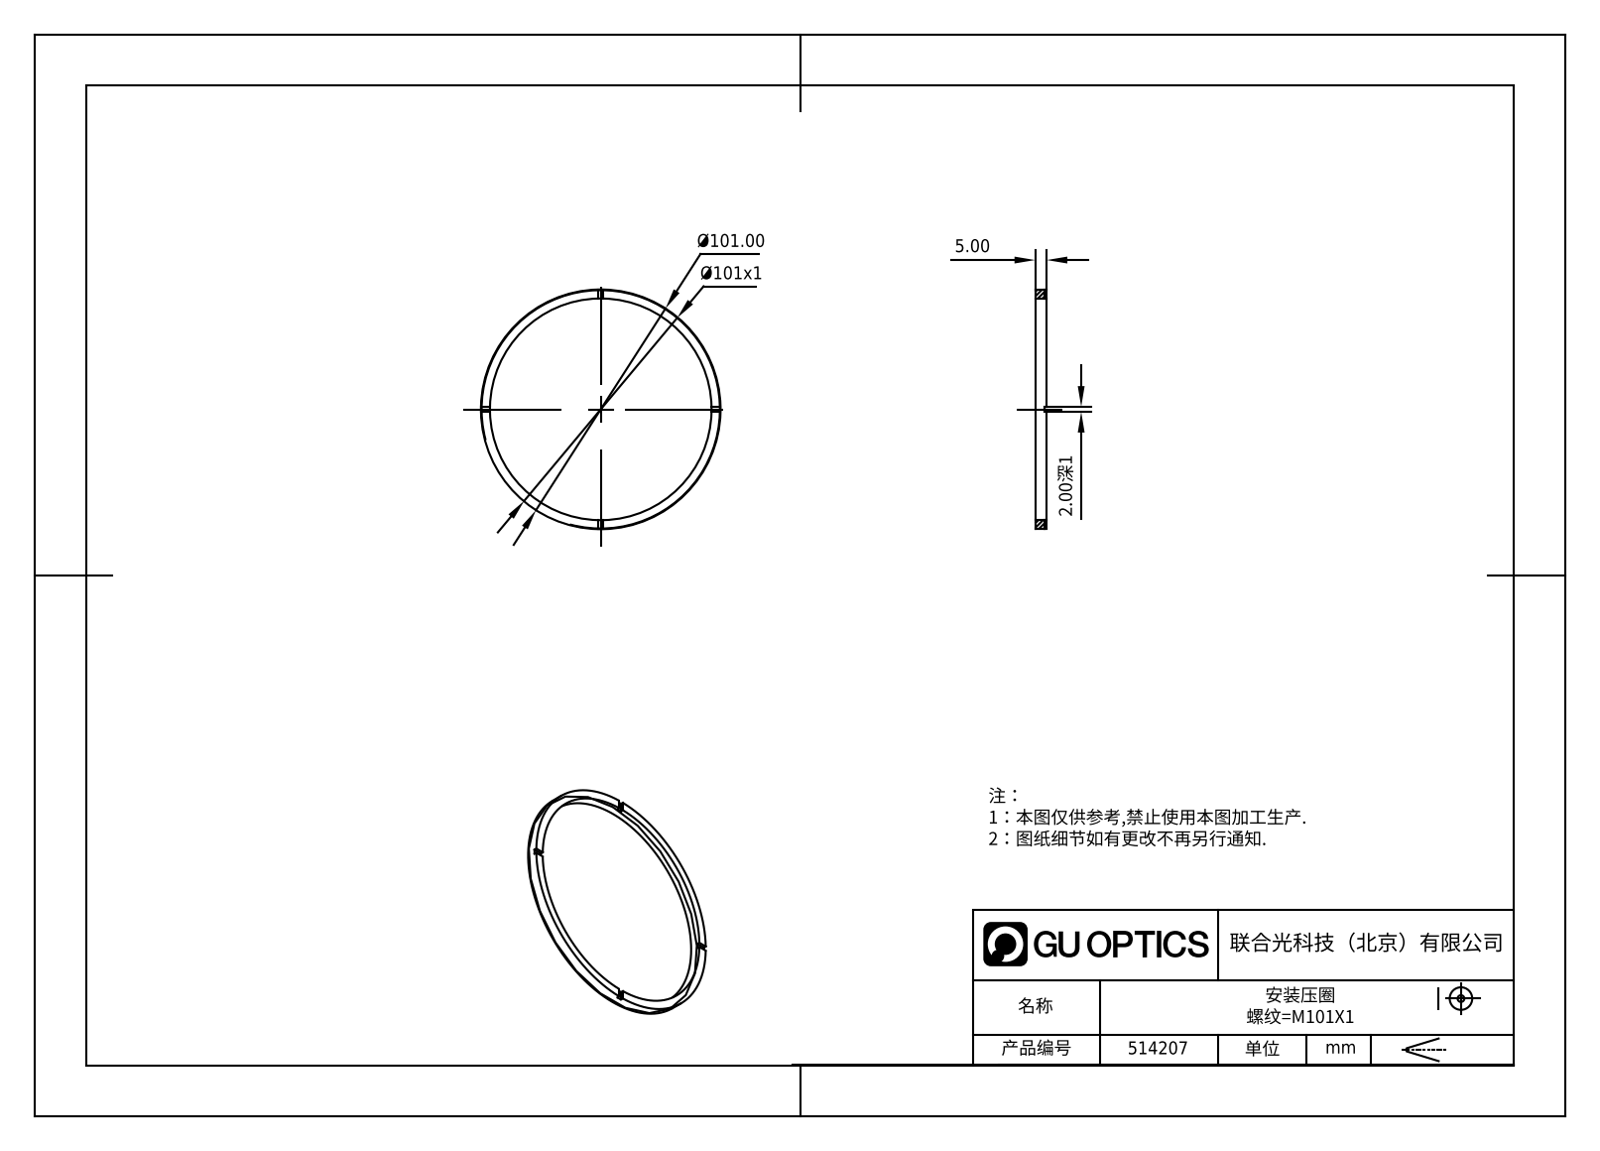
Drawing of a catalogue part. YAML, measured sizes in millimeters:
part_name: "514207"
step_written_by: "SolidWorks 2020 (CONFIG_CONTROL_DESIGN)"
units: millimeters
bodies: {solids: 1, faces: 21, planar: 17, cylindrical: 4, other: 0}
overall_size: [101, 101, 5]
volume: 6063
surface_area: 5501
round_holes:
  - {diameter: 93, count: 1}
round_bosses_or_shafts:
  - {diameter: 101, count: 1}
face_to_face_distances: [5, 4, 1, 2]
